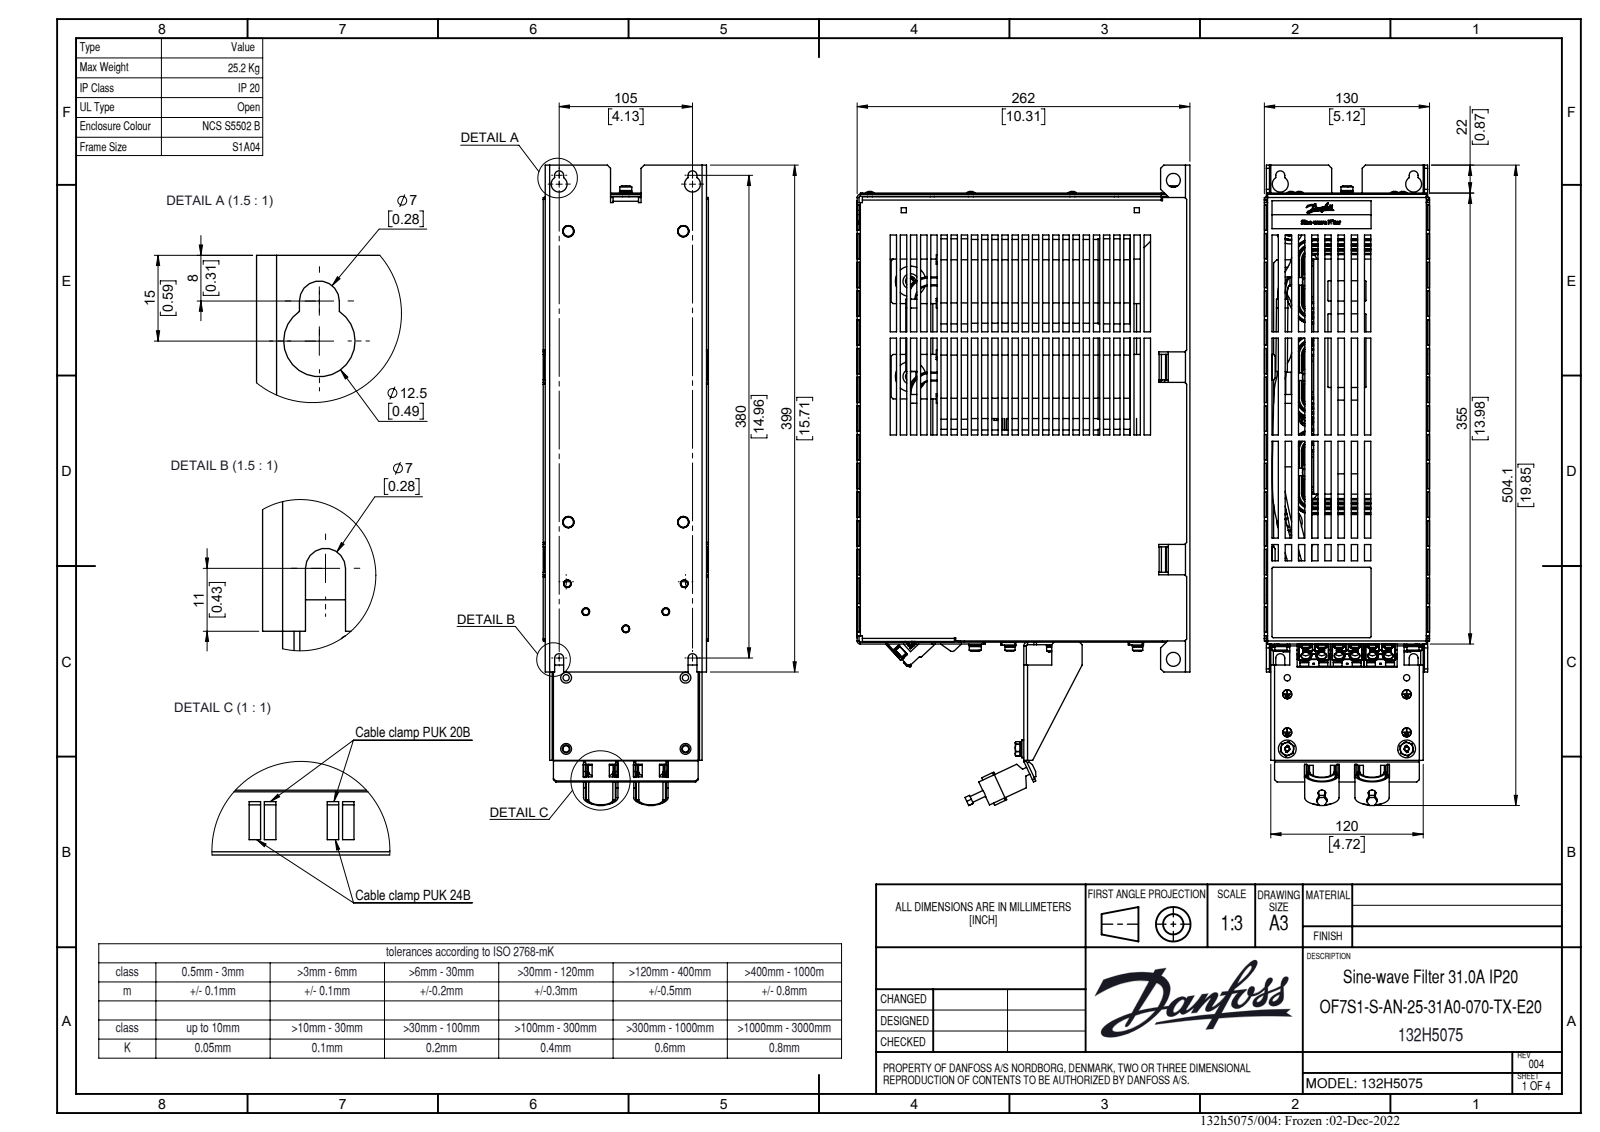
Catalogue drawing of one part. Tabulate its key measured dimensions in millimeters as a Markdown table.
| quantity | value |
| --- | --- |
| part name | 132H5075 |
| STEP written by | CREO PARAMETRIC BY PTC INC, 2020342 (CONFIG_CONTROL_DESIGN) |
| units | millimeters |
| bodies | 1 solid, 2449 faces (1962 planar, 360 cylindrical, 127 other) |
| overall size | 501.84 × 262.46 × 130 |
| volume | 11 540 000 mm³ |
| surface area | 774 523 mm² |
| round holes (diameter × count) | 3.2 × 10, 3.7 × 8, 4.2 × 6, 3.95 × 4, 4.8 × 4, 7.15 × 4, 4.5 × 3, 5.2 × 3, 6.93 × 3, 7 × 3, 7.2 × 3, 5 × 2 |
| round bosses / shafts (diameter × count) | 8 × 8, 7 × 6, 5 × 5, 8.9 × 4, 6.6 × 4, 4 × 4, 9.8 × 3, 9.5 × 3 |
| partial cylindrical surfaces (radius × count) | 1 × 29, 3 × 17, 0.4 × 12, 0.7 × 12, 2.5 × 11, 3.5 × 7, 2.4 × 4, 5.75 × 2 |
| main face-to-face distances | 2.5, 1.5, 1, 127.5, 126, 128.5, 125, 130, 127, 2 |
| hole center spacings | 94, 88, 8.73, 12.85, 13, 15.84, 16.81, 25 |
